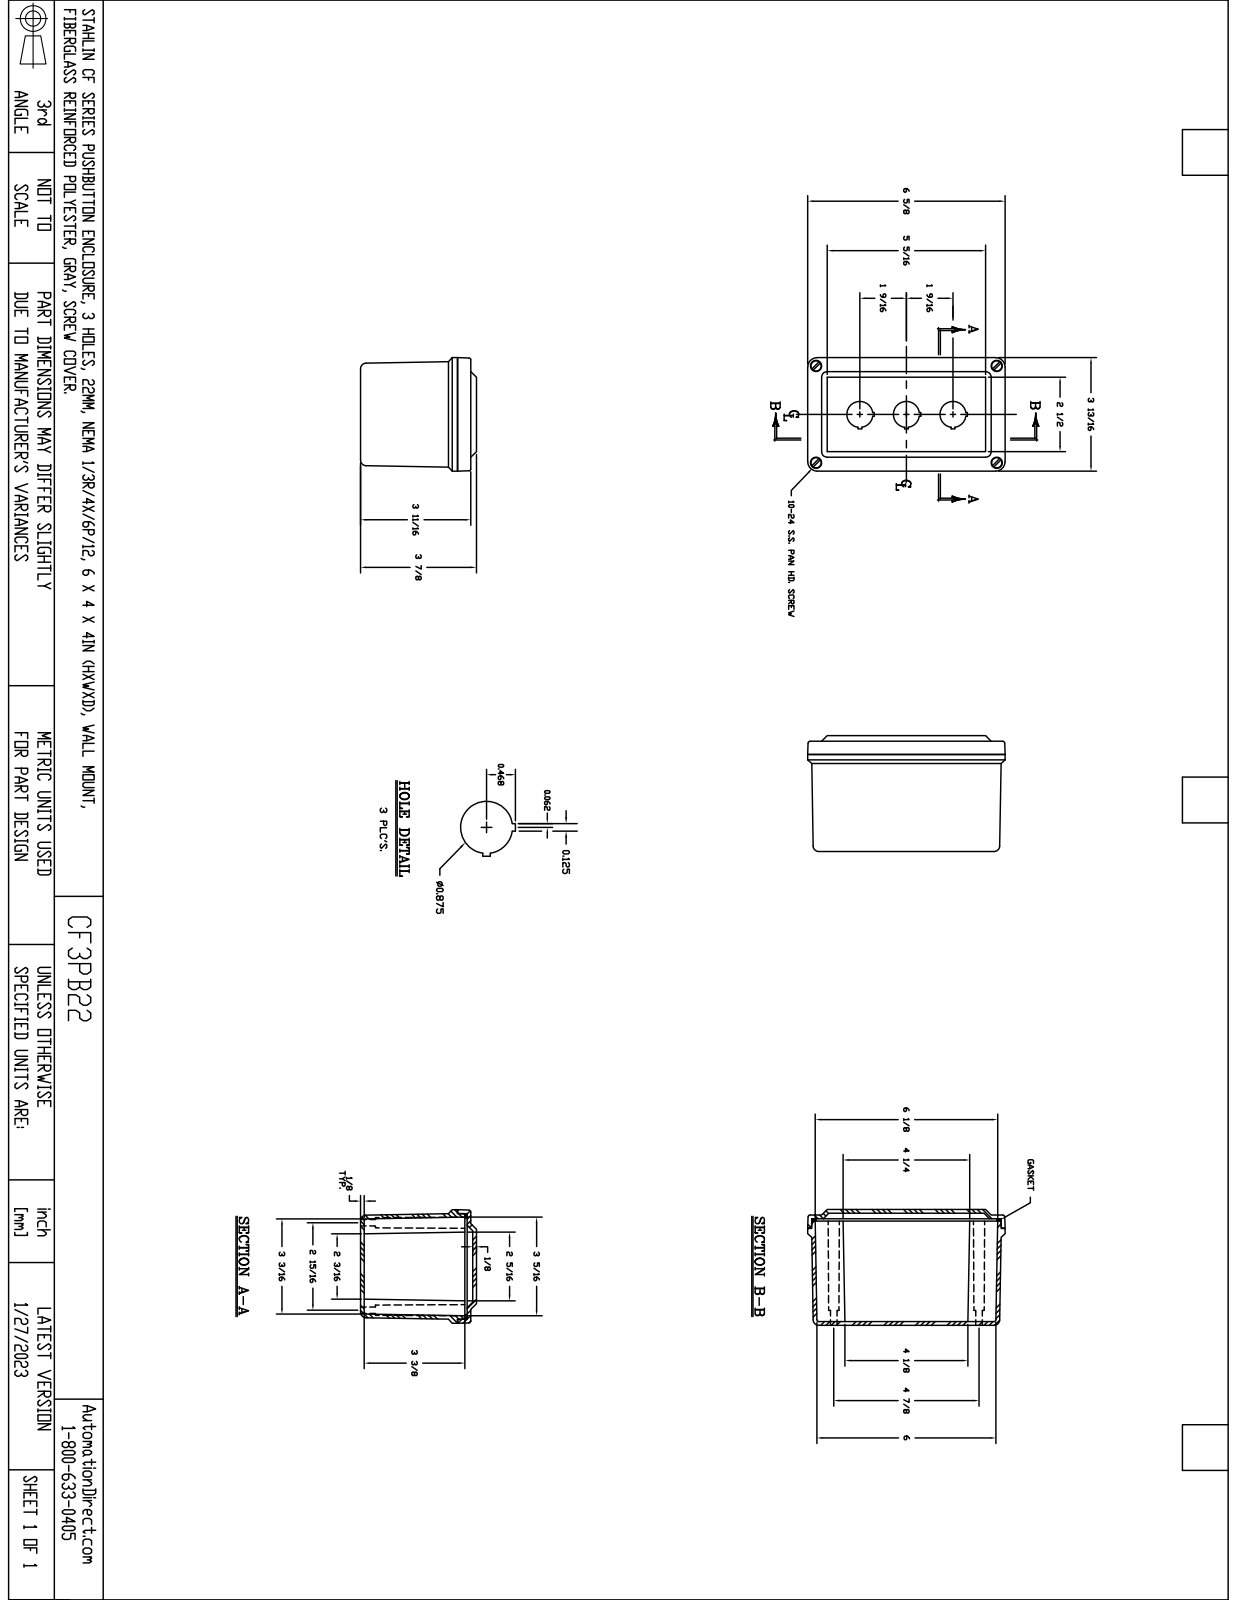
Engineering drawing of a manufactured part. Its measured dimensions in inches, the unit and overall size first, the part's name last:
Units: inches
Overall size (bounding box): 8.875 × 3.875 × 3.812
Round holes (diameter × count): ⌀0.219 ×8, ⌀0.159 ×4, ⌀0.19 ×4, ⌀0.375 ×4, ⌀0.875 ×3
Round bosses / shafts (diameter × count): ⌀0.371 ×4, ⌀0.27 ×4, ⌀0.177 ×4
Partial cylindrical surfaces — rounded edges, fillets, slot ends (radius × count): R0.031 ×20, R0.012 ×16, R0.063 ×4, R0.176 ×4, R0.188 ×4, R0.22 ×4, R0.313 ×4, R0.325 ×4
Main face-to-face distances: 0.131, 0.125, 0.125, 3.875, 3.75, 3.563, 3.75, 3.625, 0.5, 0.313
Hole centre spacings: 3.114, 8.275, 3.187, 0.576, 2.481, 3.017, 3.854, 4.422
Volume: 24.51 in³ · Surface area: 334.7 in²
Bodies: 11 solids, 403 faces (201 planar, 106 cylindrical, 96 other)
Part name (STEP PRODUCT): CO3PB22
STEP written by: SolidWorks 2018 (AUTOMOTIVE_DESIGN)
